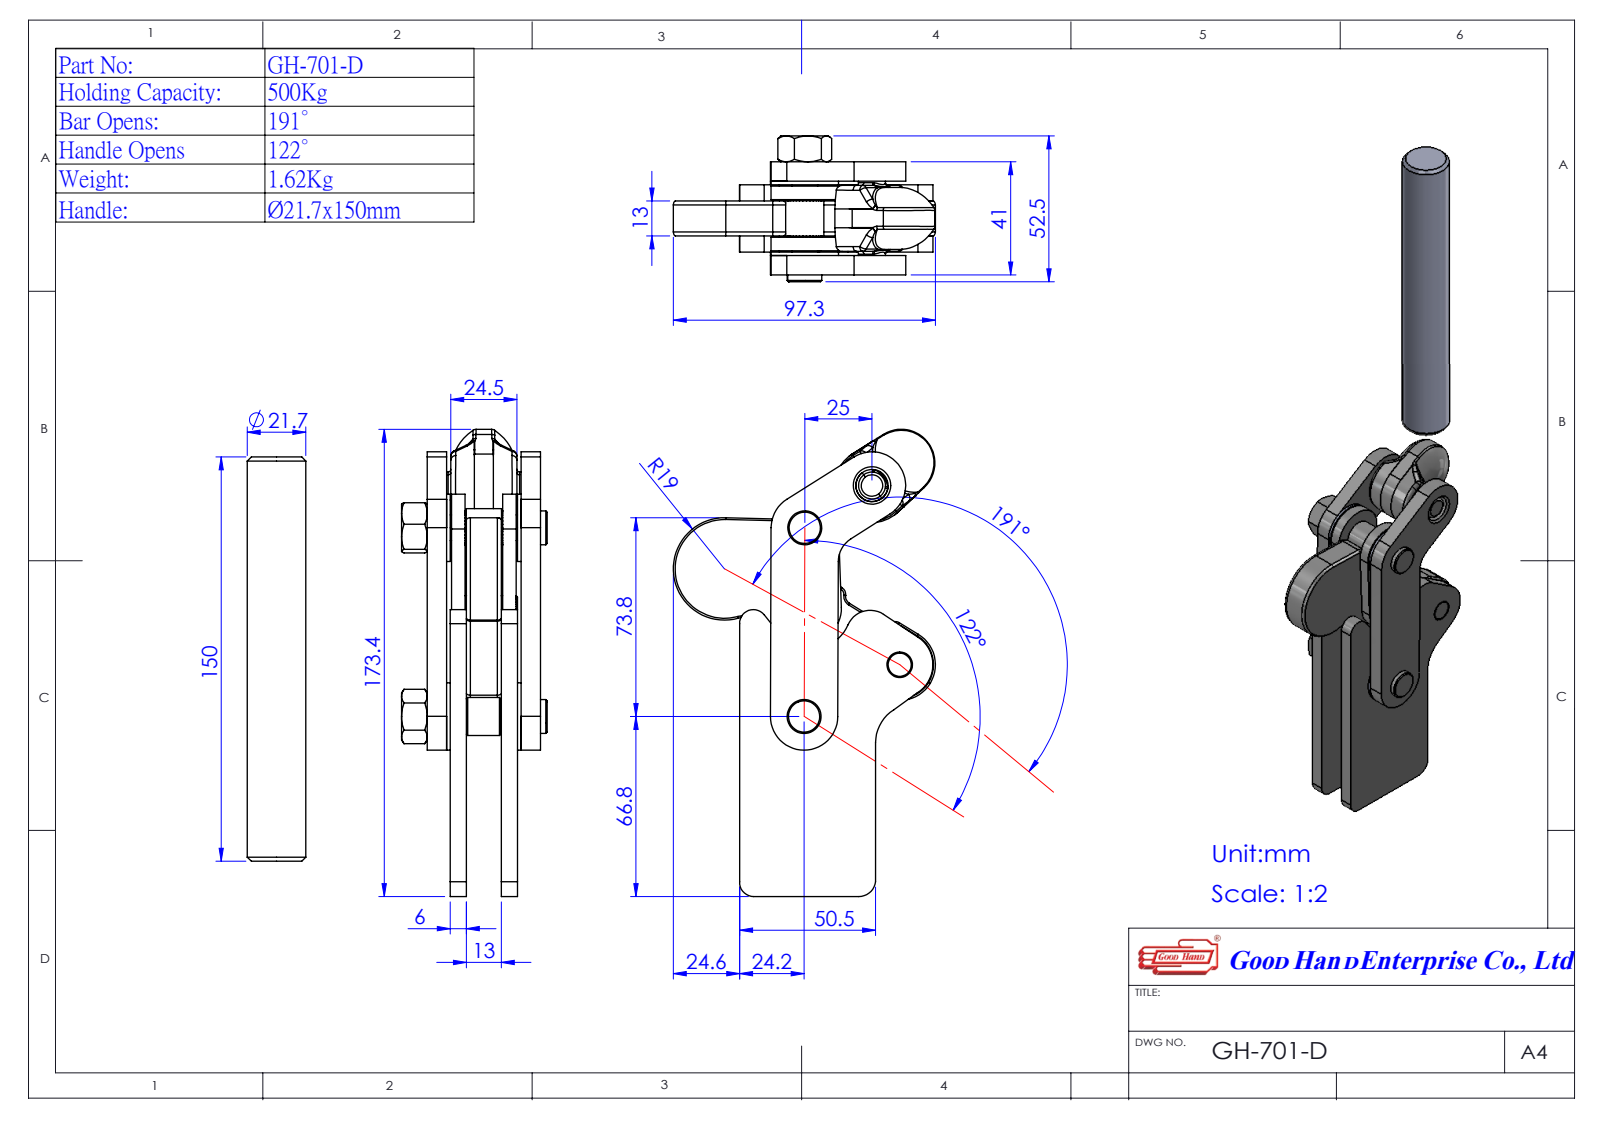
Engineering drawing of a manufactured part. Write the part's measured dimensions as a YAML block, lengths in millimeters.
part_name: "4702D152-1^GH-701-D(簡化)-1; 零件17^GH-701-D(簡化)-1; Group2^GH-701-D(簡化)-1; GH-701-D(簡化)-1 (+3 more)"
step_written_by: "SolidWorks 2016 (AUTOMOTIVE_DESIGN)"
units: millimeters
bodies: {solids: 6, faces: 197, planar: 78, cylindrical: 97, other: 22}
overall_size: [324.16, 97.66, 51.9]
volume: 208773
surface_area: 85990
round_holes:
  - {diameter: 9.5, count: 2}
  - {diameter: 9.52, count: 1}
  - {diameter: 9.6, count: 1}
  - {diameter: 11, count: 1}
  - {diameter: 12.7, count: 1}
  - {diameter: 16.9, count: 1}
round_bosses_or_shafts:
  - {diameter: 12.6, count: 2}
  - {diameter: 21.7, count: 1}
  - {diameter: 21, count: 1}
  - {diameter: 14, count: 1}
  - {diameter: 10, count: 1}
  - {diameter: 9.52, count: 1}
partial_cylinders:
  - {radius: 12.5, count: 5}
  - {radius: 3, count: 4}
  - {radius: 5, count: 2}
  - {radius: 10, count: 2}
  - {radius: 19, count: 2}
  - {radius: 5.11, count: 1}
  - {radius: 5.26, count: 1}
  - {radius: 6.3, count: 1}
face_to_face_distances: [6, 19, 13, 25, 1, 7, 26, 20, 7.7, 33.7]
hole_center_spacings: [29.49, 30, 39.97, 40.04, 40.36, 51.51, 61.88, 67.35]
